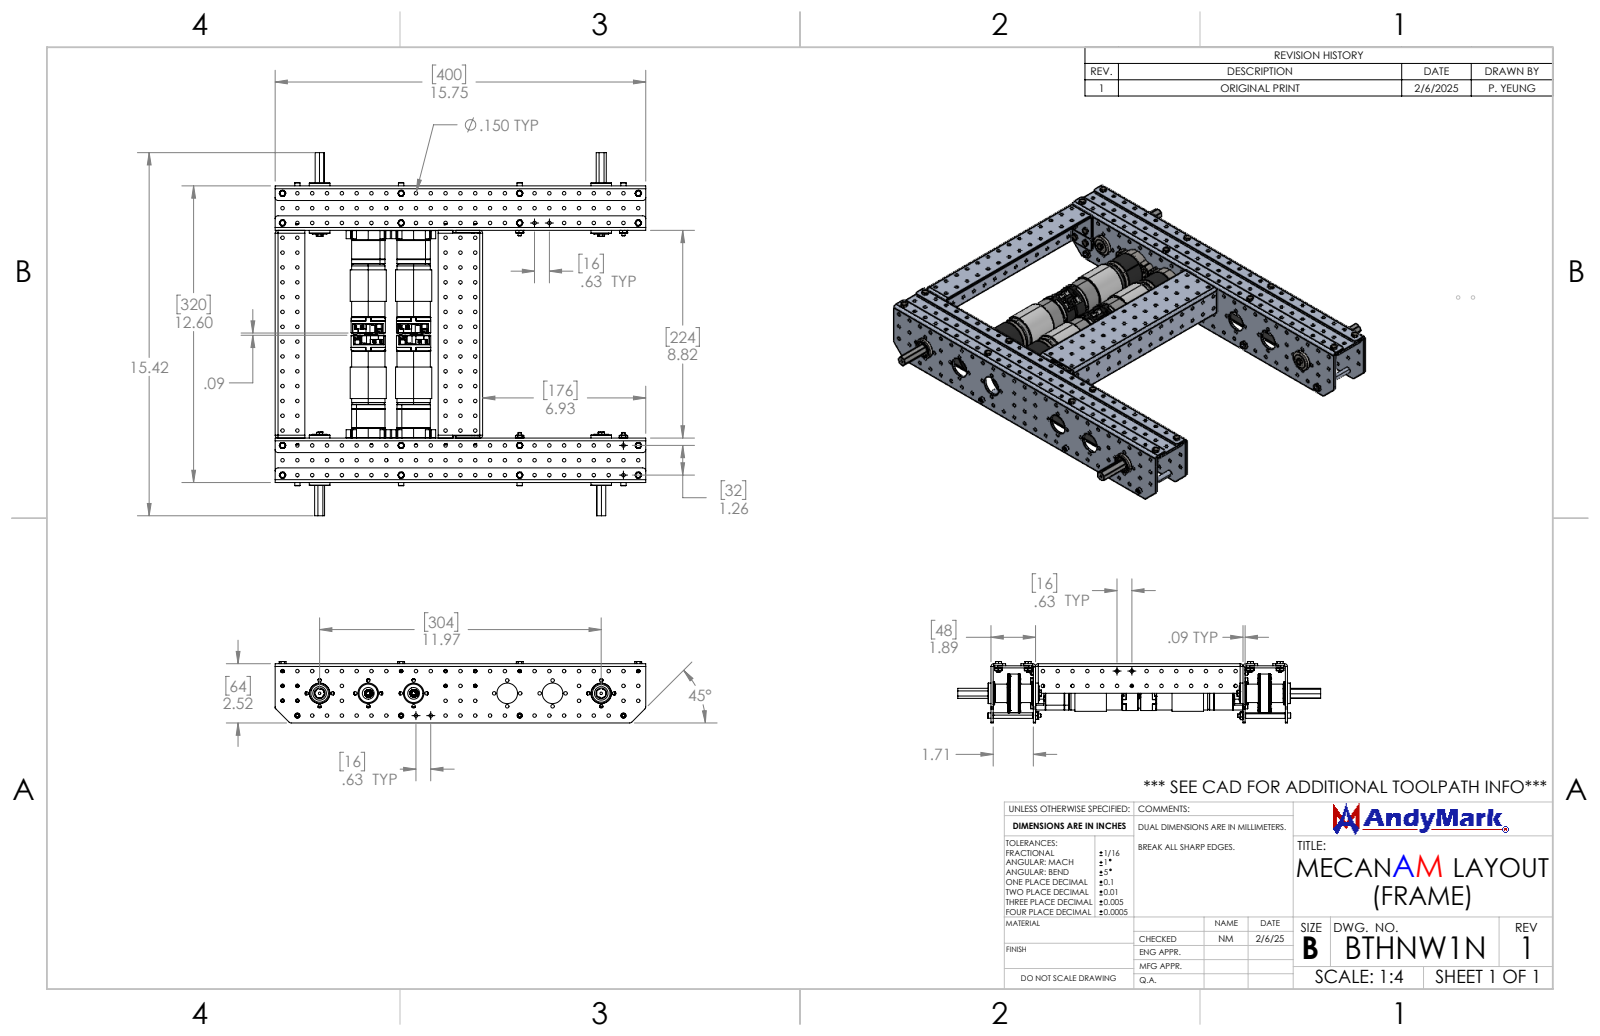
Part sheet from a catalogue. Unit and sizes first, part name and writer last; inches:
Units: inches
Overall size (bounding box): 15.748 × 15.422 × 2.613
Round holes (diameter × count): ⌀0.15 ×240, ⌀0.116 ×48, ⌀0.024 ×24, ⌀0.098 ×20, ⌀0.035 ×16, ⌀0.111 ×14, ⌀0.191 ×14, ⌀0.059 ×12, ⌀0.118 ×12, ⌀0.157 ×12, ⌀0.159 ×10, ⌀0.016 ×8
Round bosses / shafts (diameter × count): ⌀0.028 ×24, ⌀0.02 ×24, ⌀0.217 ×16, ⌀0.118 ×16, ⌀0.15 ×12, ⌀0.138 ×12, ⌀0.157 ×8, ⌀0.093 ×8
Partial cylindrical surfaces — rounded edges, fillets, slot ends (radius × count): R0.01 ×640, R0.012 ×384, R0.017 ×384, R0.017 ×384, R0.054 ×384, R0.069 ×384, R0.089 ×384, R0.112 ×384
Main face-to-face distances: 10.709, 0.09, 0.09, 1.71, 1.8, 1.8, 1.89, 8.819, 8.909, 10.619
Hole centre spacings: 0.63, 1.26, 1.89, 3.15, 2.52, 2.271, 3.78, 1.992
Volume: 62.81 in³ · Surface area: 1 221 in²
Bodies: 344 solids, 68948 faces (9195 planar, 18791 cylindrical, 40962 other)
Part name (STEP PRODUCT): am-3104c NeveRest Hex Bare Motor; am-3104c_cap NeveRest Hex Encoder Cap._am-3104c_cap NeveRest Hex Encoder Cap; am-5550g_0100_014 NeveRest Hex 13.7 Gearbox, 1IN Shaft; am-0028 3-8 ID Flanged Bearing (+8 more)
STEP written by: SolidWorks 2024 (AUTOMOTIVE_DESIGN)
